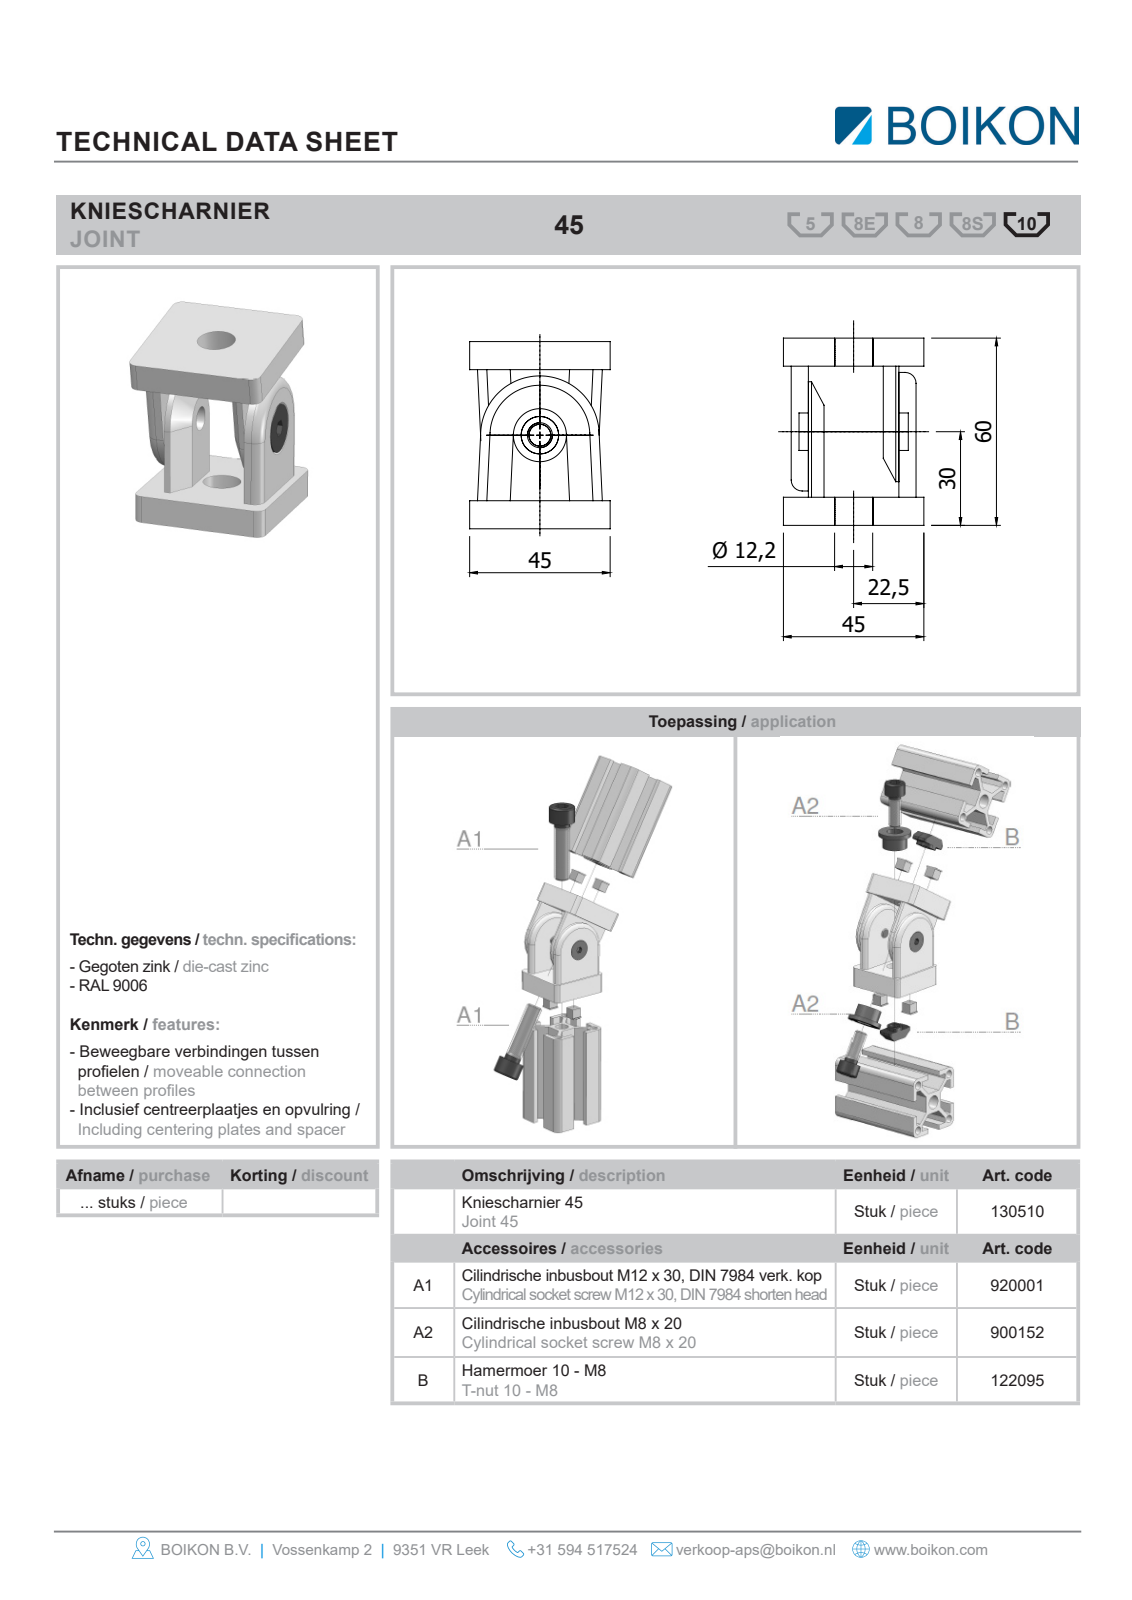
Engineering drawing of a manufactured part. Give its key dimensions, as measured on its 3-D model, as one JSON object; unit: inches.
{"part_name": "Root; 130510Scharnier 45BOIKON; 900610Verz. inbusbout DIN 7991 EV M8 x 10Countersunk head bolts0", "step_written_by": "HiCAD 2013 1802.4 Build 509 (AUTOMOTIVE_DESIGN)", "units": "inches", "bodies": {"solids": 4, "faces": 96, "planar": 54, "cylindrical": 32, "other": 10}, "overall_size": [2.362, 1.772, 1.772], "volume_in3": 3.528, "surface_area_in2": 35.22, "round_holes": [[0.315, 1], [0.354, 1], [0.492, 1], [1.024, 1]], "round_bosses_or_shafts": [[1.339, 1], [1.26, 1], [0.63, 1], [0.255, 1]], "partial_cylinders_radius": [[0.118, 4], [0.138, 4]], "face_to_face_distances": [0.354, 2.008, 2.362, 1.102, 1.339, 0.236, 1.654, 0.098, 0.335, 1.437]}
